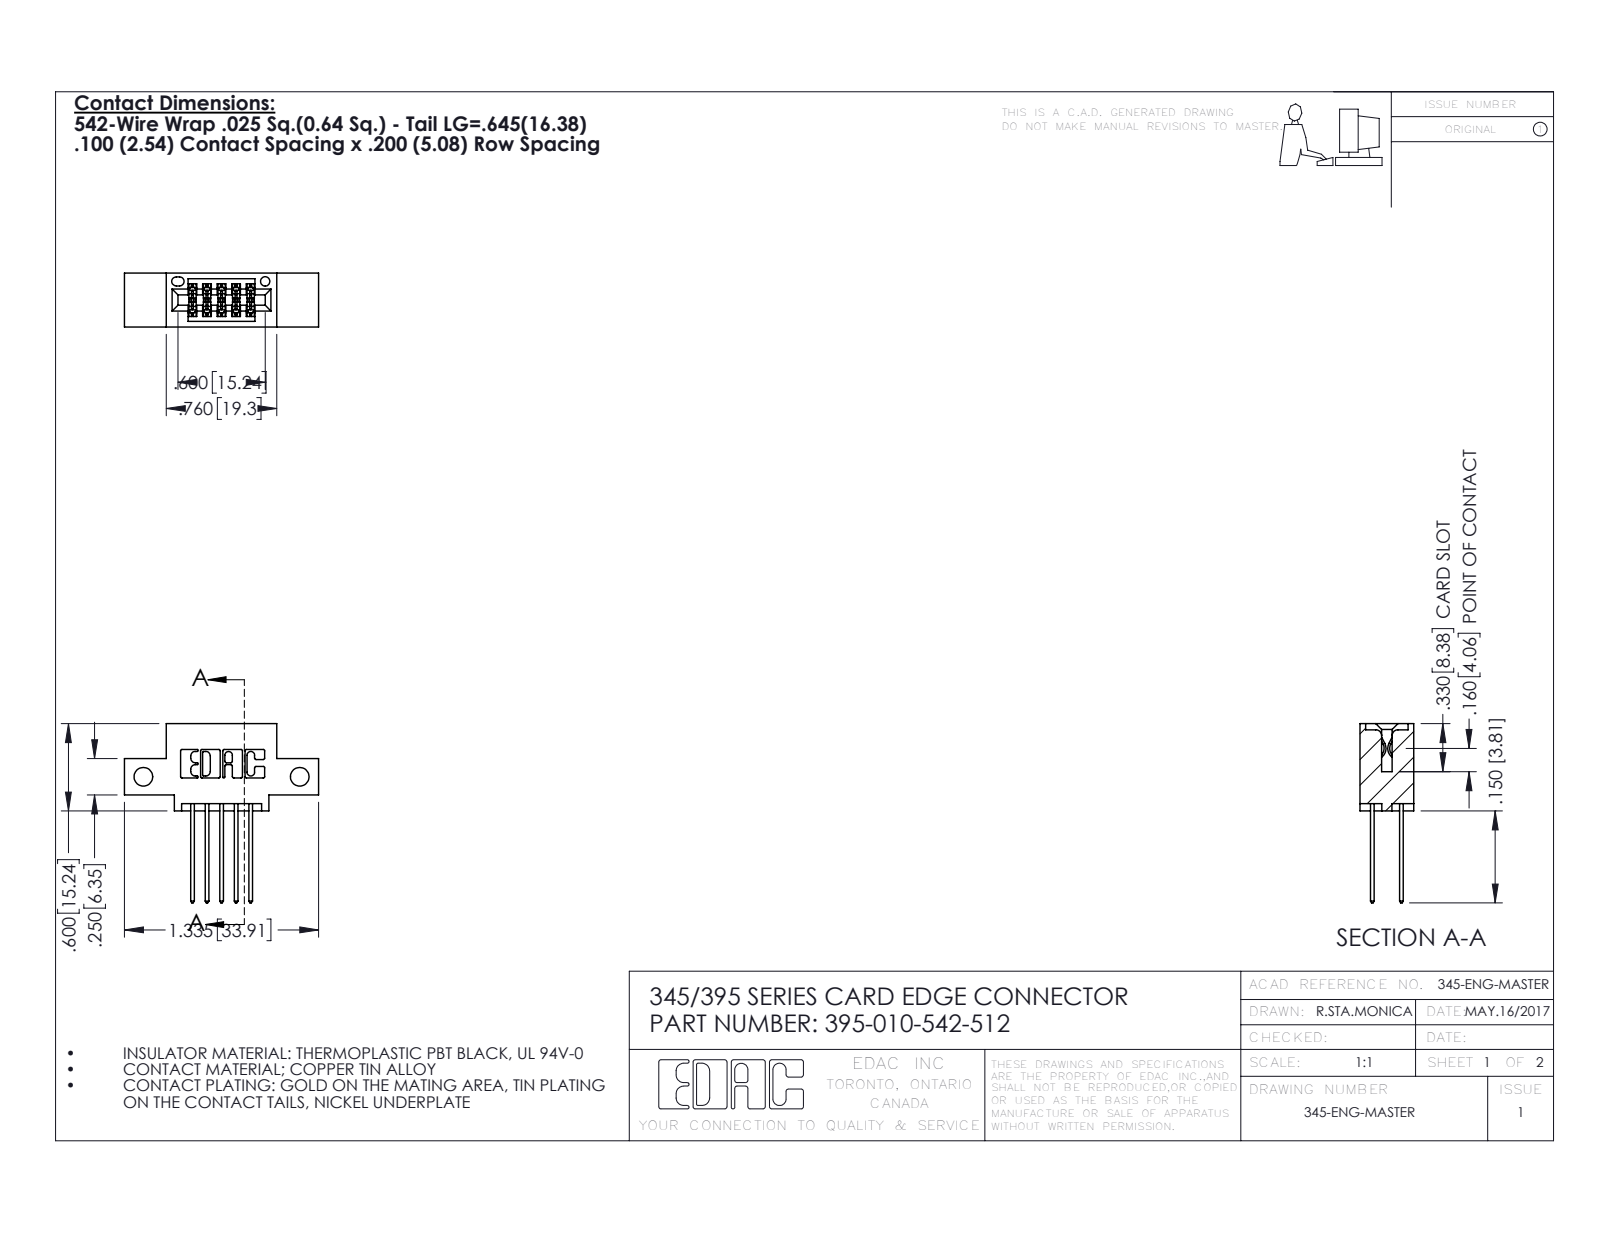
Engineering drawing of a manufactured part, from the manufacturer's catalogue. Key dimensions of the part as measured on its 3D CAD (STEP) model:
Part name (STEP PRODUCT): 395-010-542-512; 345-292-001_345-293-142; 345 Part_0.110 Offset - Side Mount
STEP written by: SolidWorks 2016 (CONFIG_CONTROL_DESIGN)
Units: inches
Bodies: 11 solids, 630 faces (414 planar, 216 cylindrical, 0 other)
Overall size (bounding box): 1.335 × 1.232 × 0.37
Volume: 0.173 in³ · Surface area: 5.659 in²
Round holes (diameter × count): ⌀0.128 ×2, ⌀0.064 ×1
Partial cylindrical surfaces — rounded edges, fillets, slot ends (radius × count): R0.01 ×22, R0.006 ×15, R0.01 ×10, R0.007 ×6, R0.031 ×6, R0.026 ×3, R0.014 ×2, R0.019 ×2
Main face-to-face distances: 0.2, 0.298, 0.072, 0.37, 0.1, 0.098, 0.272, 0.025, 0.25, 0.225
Hole centre spacings: 1.075
